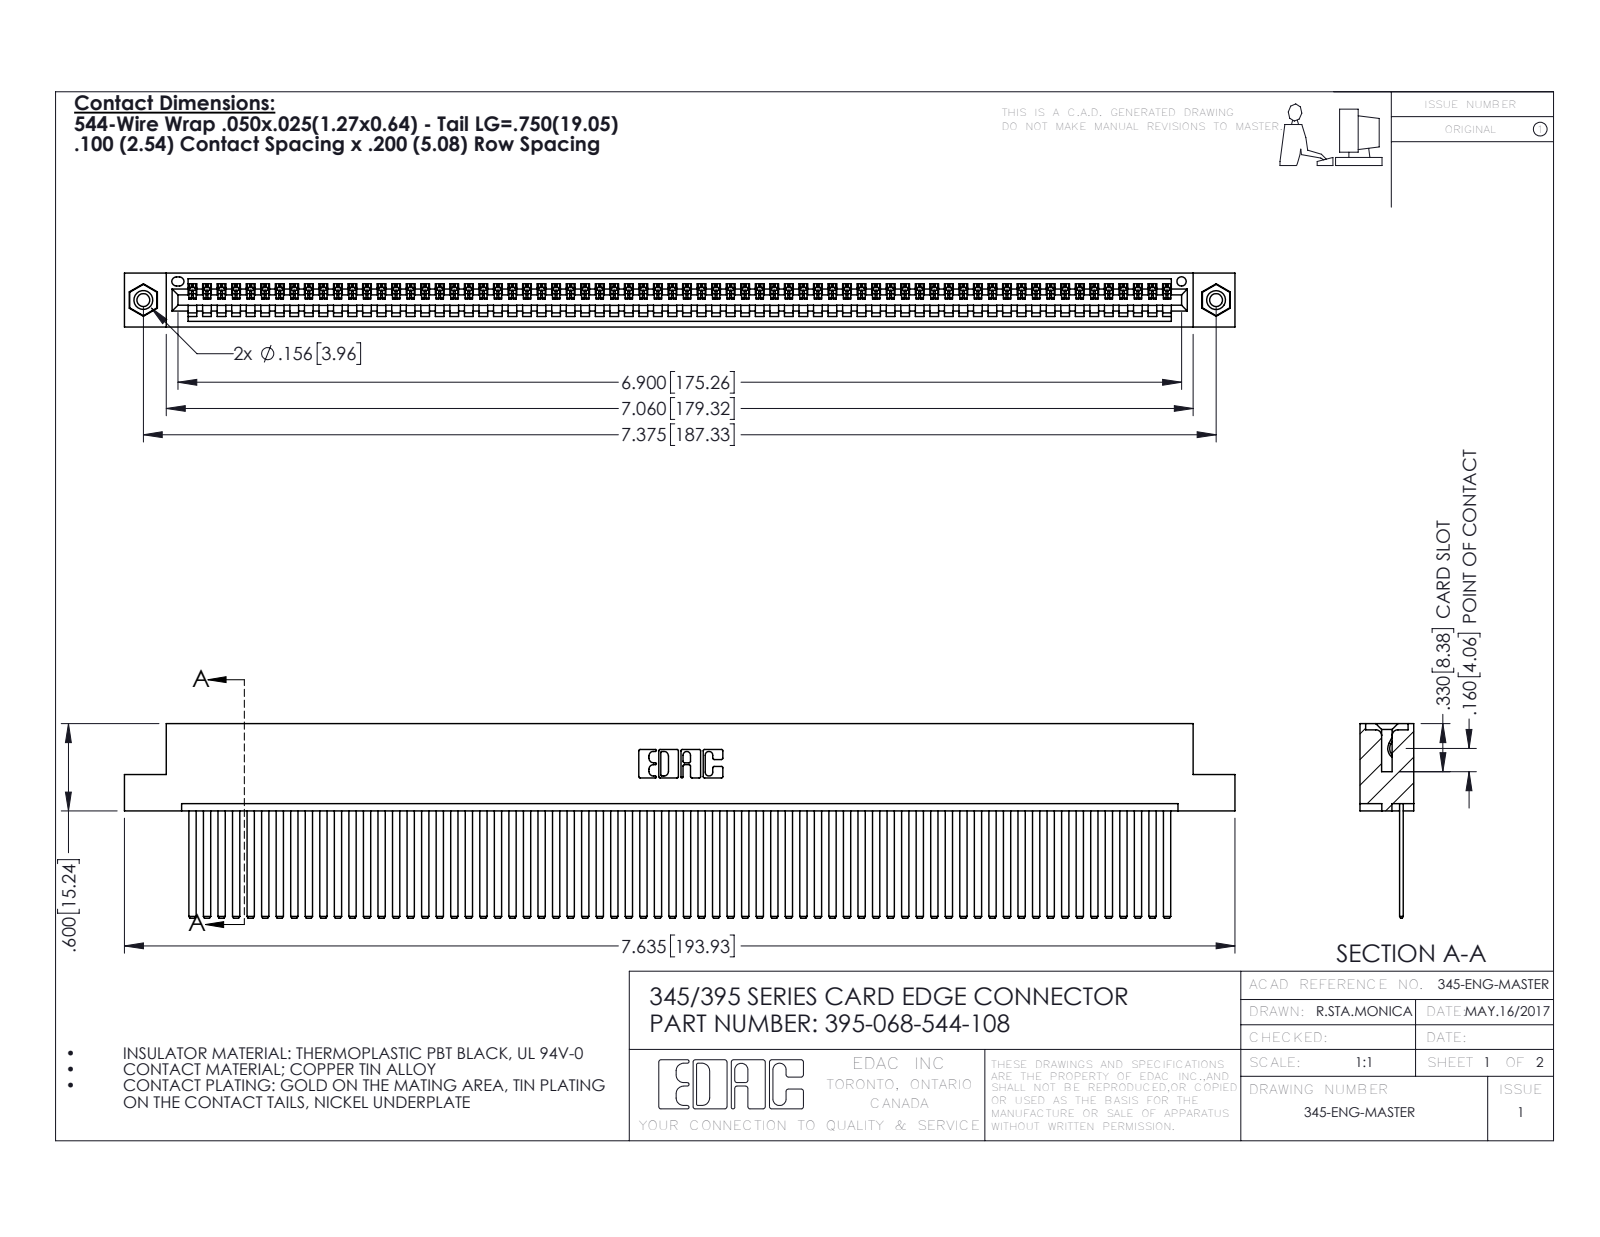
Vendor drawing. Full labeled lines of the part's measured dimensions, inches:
Part name (STEP PRODUCT): 345-250-001_345-250-003-102; 345-292-001_345-293-144; 345 Part_Flush Mounting Lugs - 0.156 Dia-TI; 395-068-544-108
STEP written by: SolidWorks 2016 (CONFIG_CONTROL_DESIGN)
Units: inches
Bodies: 71 solids, 3722 faces (2560 planar, 1146 cylindrical, 16 other)
Overall size (bounding box): 7.635 × 1.337 × 0.37
Volume: 1.185 in³ · Surface area: 44.23 in²
Round holes (diameter × count): ⌀0.089 ×2, ⌀0.125 ×2, ⌀0.156 ×2, ⌀0.064 ×1
Round bosses / shafts (diameter × count): ⌀0.155 ×2
Partial cylindrical surfaces — rounded edges, fillets, slot ends (radius × count): R0.006 ×136, R0.01 ×22, R0.007 ×6, R0.031 ×6, R0.026 ×3, R0.031 ×2, R0.04 ×2, R0.014 ×1
Main face-to-face distances: 0.072, 0.298, 0.025, 0.098, 0.272, 0.37, 0.2, 0.225, 0.149, 0.072
Hole centre spacings: 0.27, 7.139, 7.375
